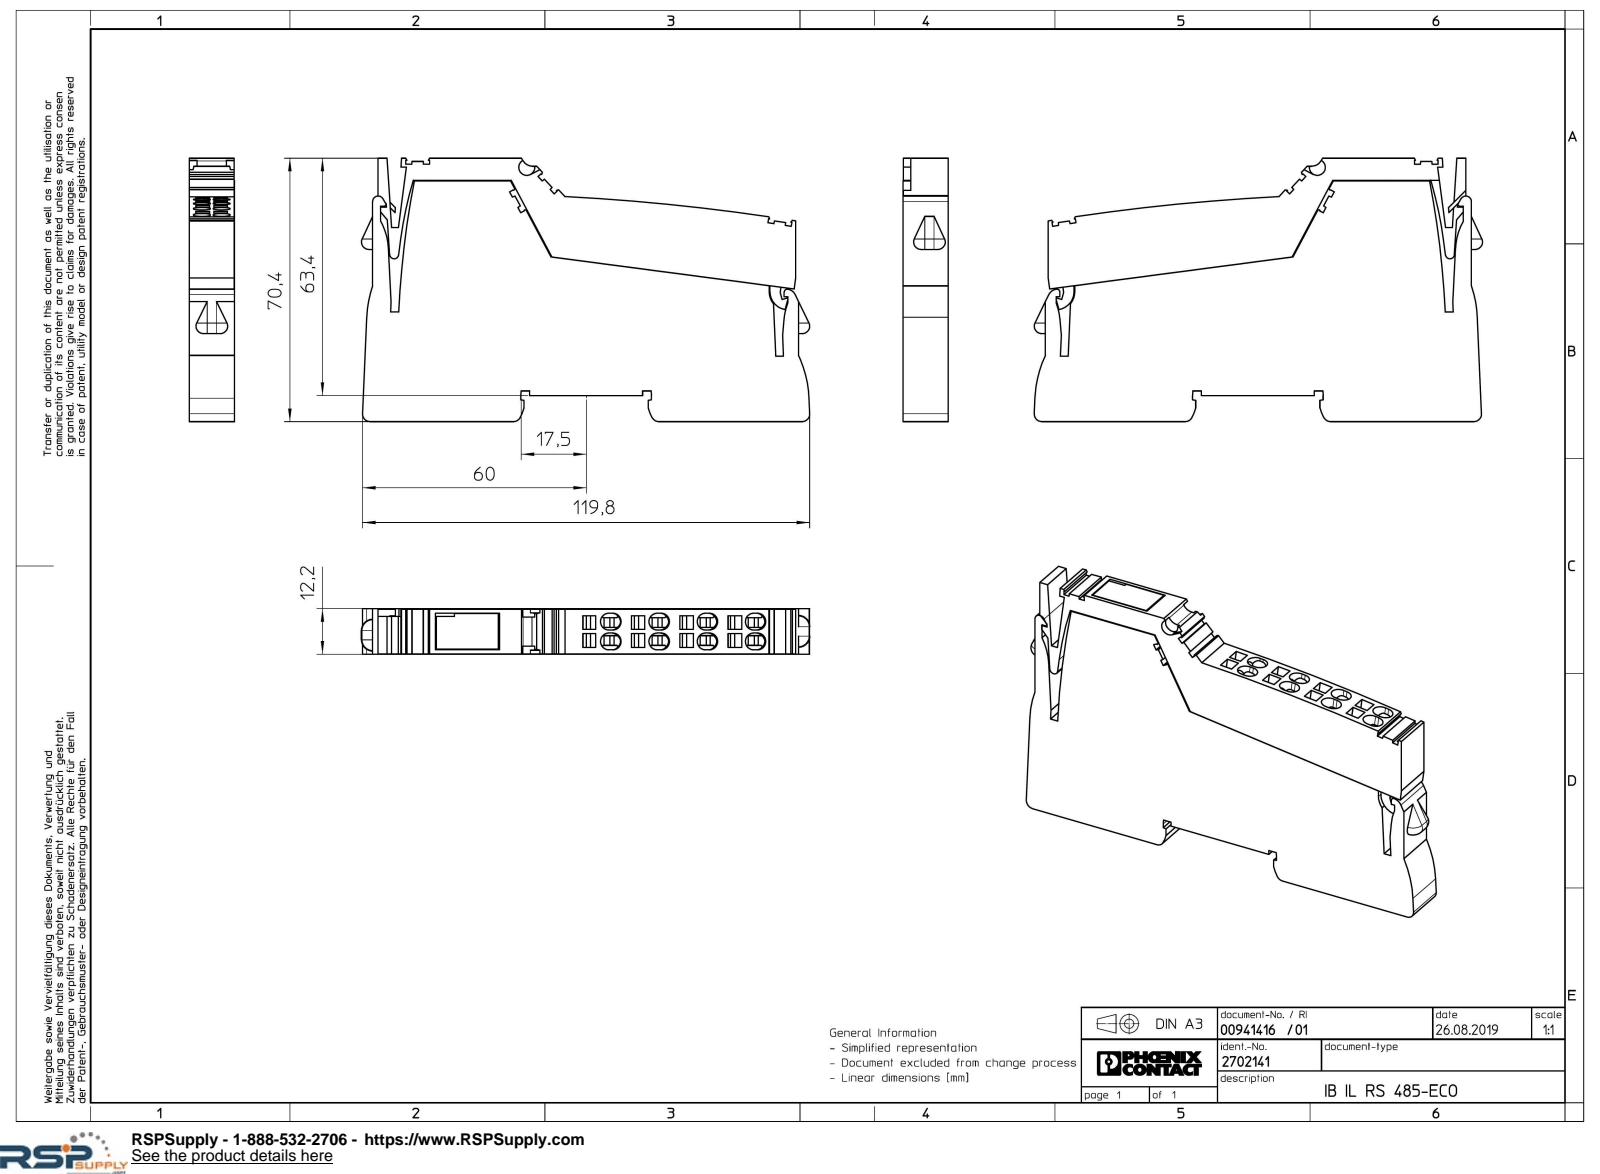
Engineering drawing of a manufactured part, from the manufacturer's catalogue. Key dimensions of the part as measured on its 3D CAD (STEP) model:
Part name (STEP PRODUCT): L-L_ST_GN_6021-select; L_L_2_GEH_GN_6021-select; L_L_LWL_OG_HKS_7K_AUSSEN-select; IB_IL_RS_485_ECO-select
STEP written by: Creo Elements/Direct Modeling 20.1A 29-Sep-2018 (C) Parametric Technology GmbH (AUTOMOTIVE_DESIGN)
Units: millimetres
Bodies: 3 solids, 598 faces (501 planar, 61 cylindrical, 36 other)
Overall size (bounding box): 120.11 × 70.43 × 12.15
Volume: 79 605 mm³ · Surface area: 28 771 mm²
Round holes (diameter × count): ⌀1.2 ×6
Partial cylindrical surfaces — rounded edges, fillets, slot ends (radius × count): R2.25 ×16, R2 ×6, R0.15 ×2, R0.6 ×2, R8.5 ×2, R9.5 ×2, R16.7 ×2, R30 ×2
Main face-to-face distances: 12.15, 12.1, 12.05, 12, 25.99, 13, 3.3, 64.4, 12.99, 4.8
Hole centre spacings: 13, 13.86, 4.8, 26, 26.44
